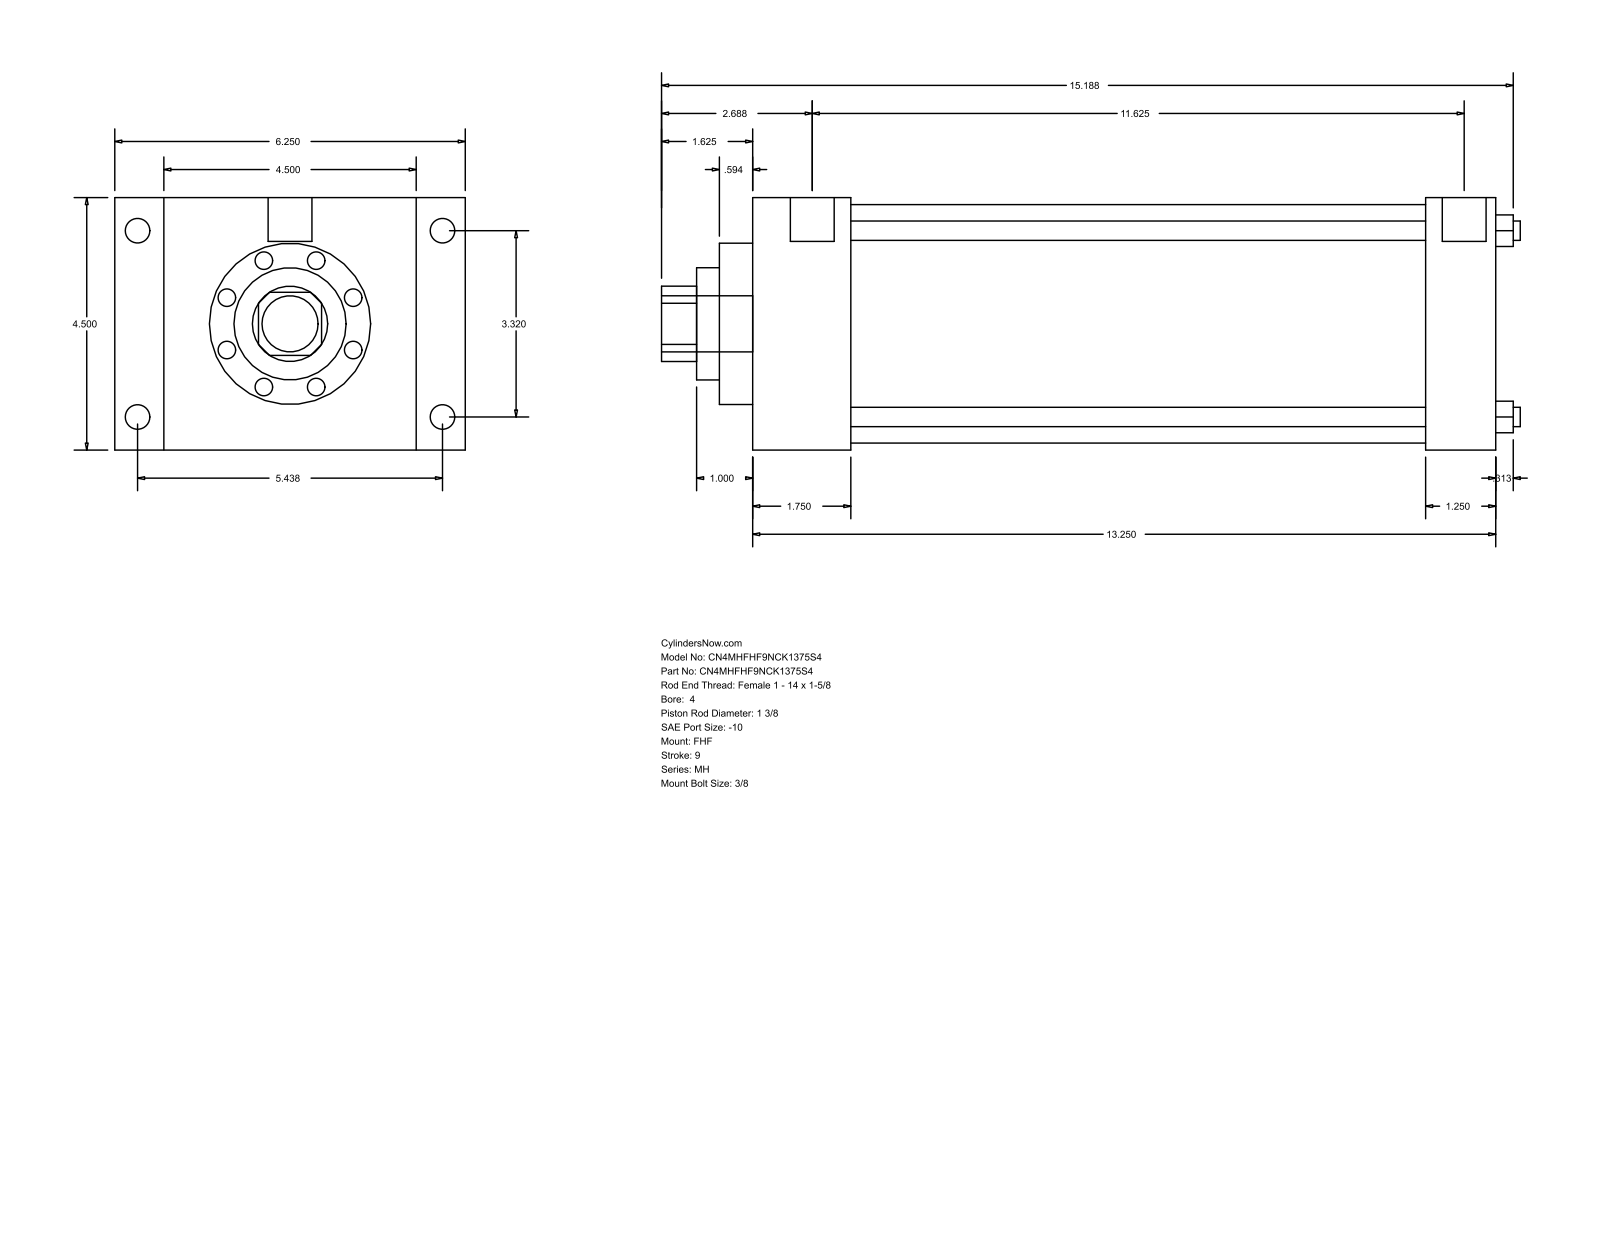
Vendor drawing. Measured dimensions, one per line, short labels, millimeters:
name: MH_FHF__0400_1.375
written by: GSSL Pune (CONFIG_CONTROL_DESIGN)
unit: mm
bodies: 0 solids, 90 faces (61 planar, 29 cylindrical, 0 other)
size: 388.94 × 158.75 × 114.3
holes: 4× ⌀8.76, 1× ⌀34.92, 1× ⌀50.8, 1× ⌀73.03, 1× ⌀107.95
bosses: 4× ⌀11.13, 4× ⌀8.73, 2× ⌀19.84, 1× ⌀25.4
rounds: 1× R17.06
face distances: 114.3, 336.55, 44.45, 292.1, 22.23, 136.53, 158.76, 304.8, 260.35, 31.75
hole spacings: 59.62, 84.32, 119.25
